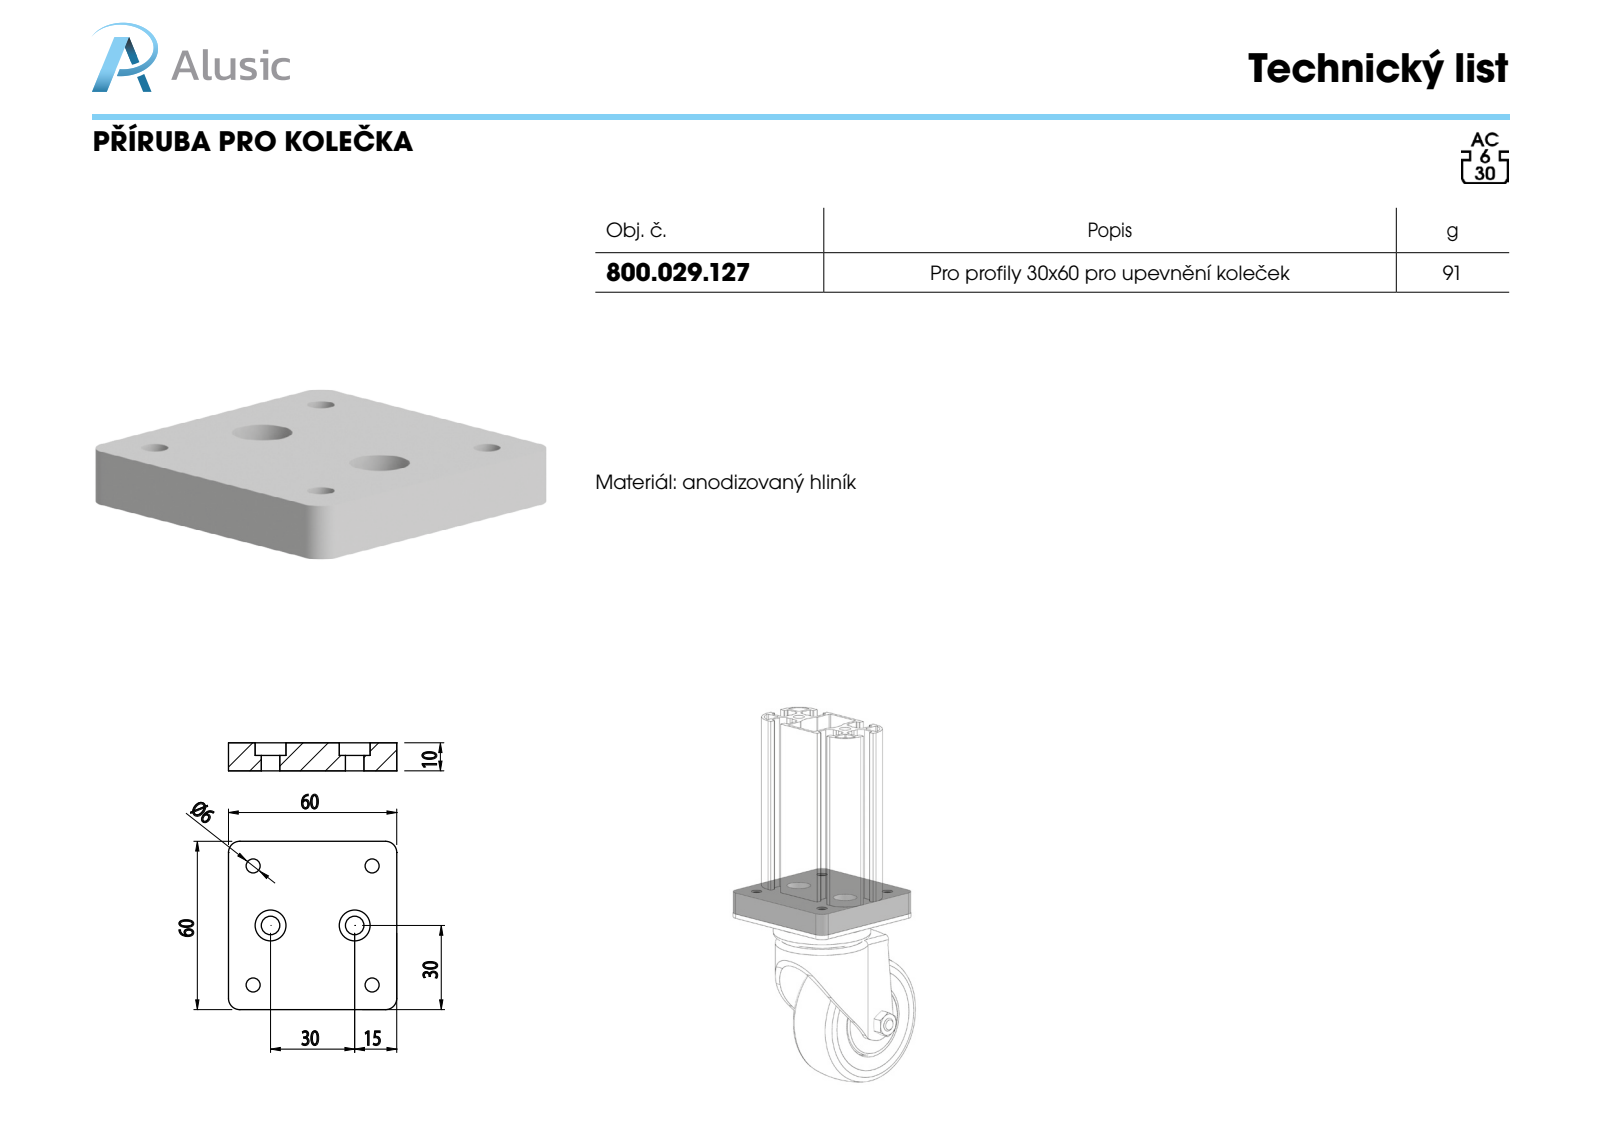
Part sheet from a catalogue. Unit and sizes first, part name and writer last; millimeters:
Units: millimetres
Overall size (bounding box): 60 × 60 × 10
Round holes (diameter × count): ⌀5 ×4, ⌀6.6 ×2, ⌀11 ×2
Partial cylindrical surfaces — rounded edges, fillets, slot ends (radius × count): R4 ×4
Main face-to-face distances: 10, 60, 5.5, 4.5
Hole centre spacings: 22.1, 41.96, 42.42, 59.99, 30
Volume: 33 846 mm³ · Surface area: 10 377 mm²
Bodies: 1 solid, 28 faces (8 planar, 20 cylindrical, 0 other)
Part name (STEP PRODUCT): 800.029.127
STEP written by: SolidWorks 2012 (CONFIG_CONTROL_DESIGN)
